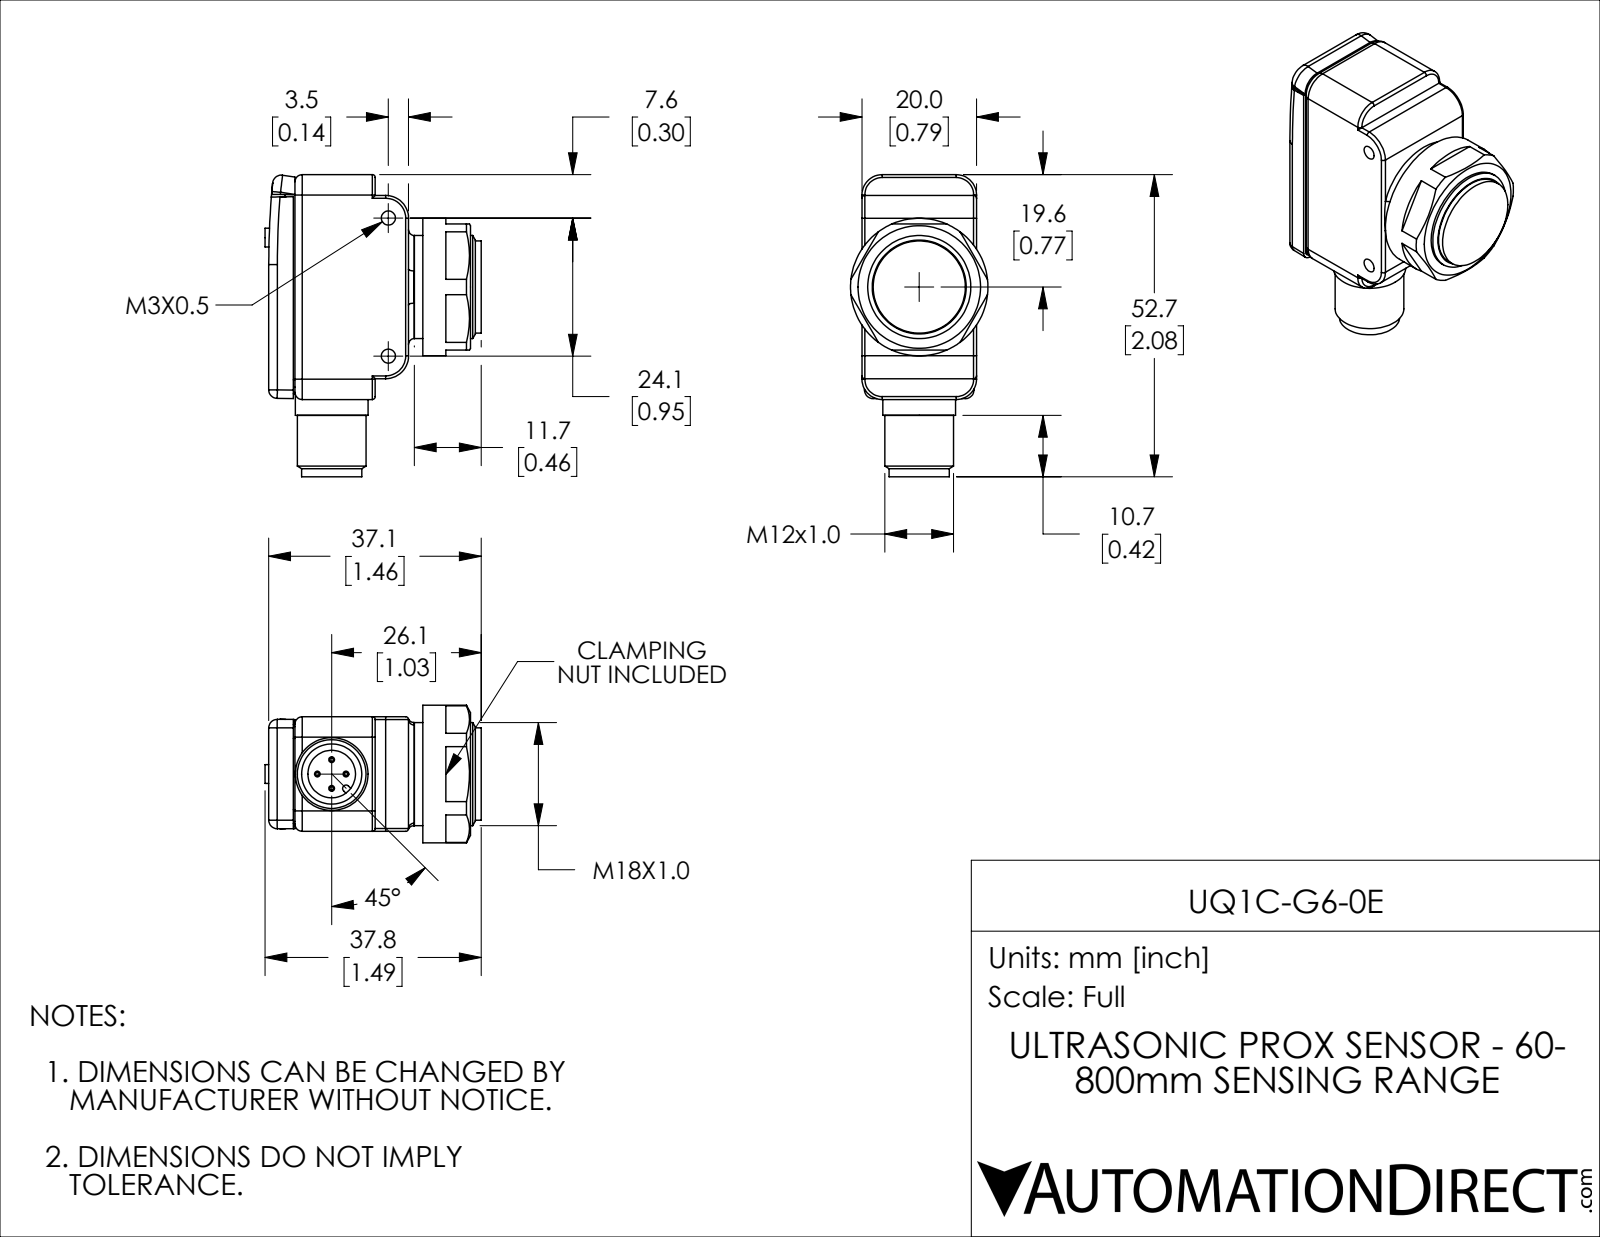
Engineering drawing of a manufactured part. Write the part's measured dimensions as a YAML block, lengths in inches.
part_name: "UQ1C-G6-0E"
step_written_by: "SolidWorks 2018 (AUTOMOTIVE_DESIGN)"
units: inches
bodies: {solids: 7, faces: 203, planar: 81, cylindrical: 72, other: 50}
overall_size: [2.076, 1.486, 0.945]
volume: 1.389
surface_area: 17.13
round_holes:
  - {diameter: 0.097, count: 2}
  - {diameter: 0.13, count: 1}
  - {diameter: 0.327, count: 1}
round_bosses_or_shafts:
  - {diameter: 0.039, count: 4}
  - {diameter: 0.945, count: 1}
  - {diameter: 0.709, count: 1}
  - {diameter: 0.634, count: 1}
  - {diameter: 0.5, count: 1}
  - {diameter: 0.472, count: 1}
  - {diameter: 0.413, count: 1}
partial_cylinders:
  - {radius: 0.02, count: 10}
  - {radius: 0.059, count: 6}
  - {radius: 0.049, count: 4}
  - {radius: 0.14, count: 4}
  - {radius: 0.118, count: 2}
  - {radius: 0.157, count: 2}
  - {radius: 5.906, count: 2}
  - {radius: 0.024, count: 1}
face_to_face_distances: [0.091, 0.787, 0.911, 0.82, 0.09, 0.181, 1.001, 0.459, 1.46, 1.37]
hole_center_spacings: [0.949]
